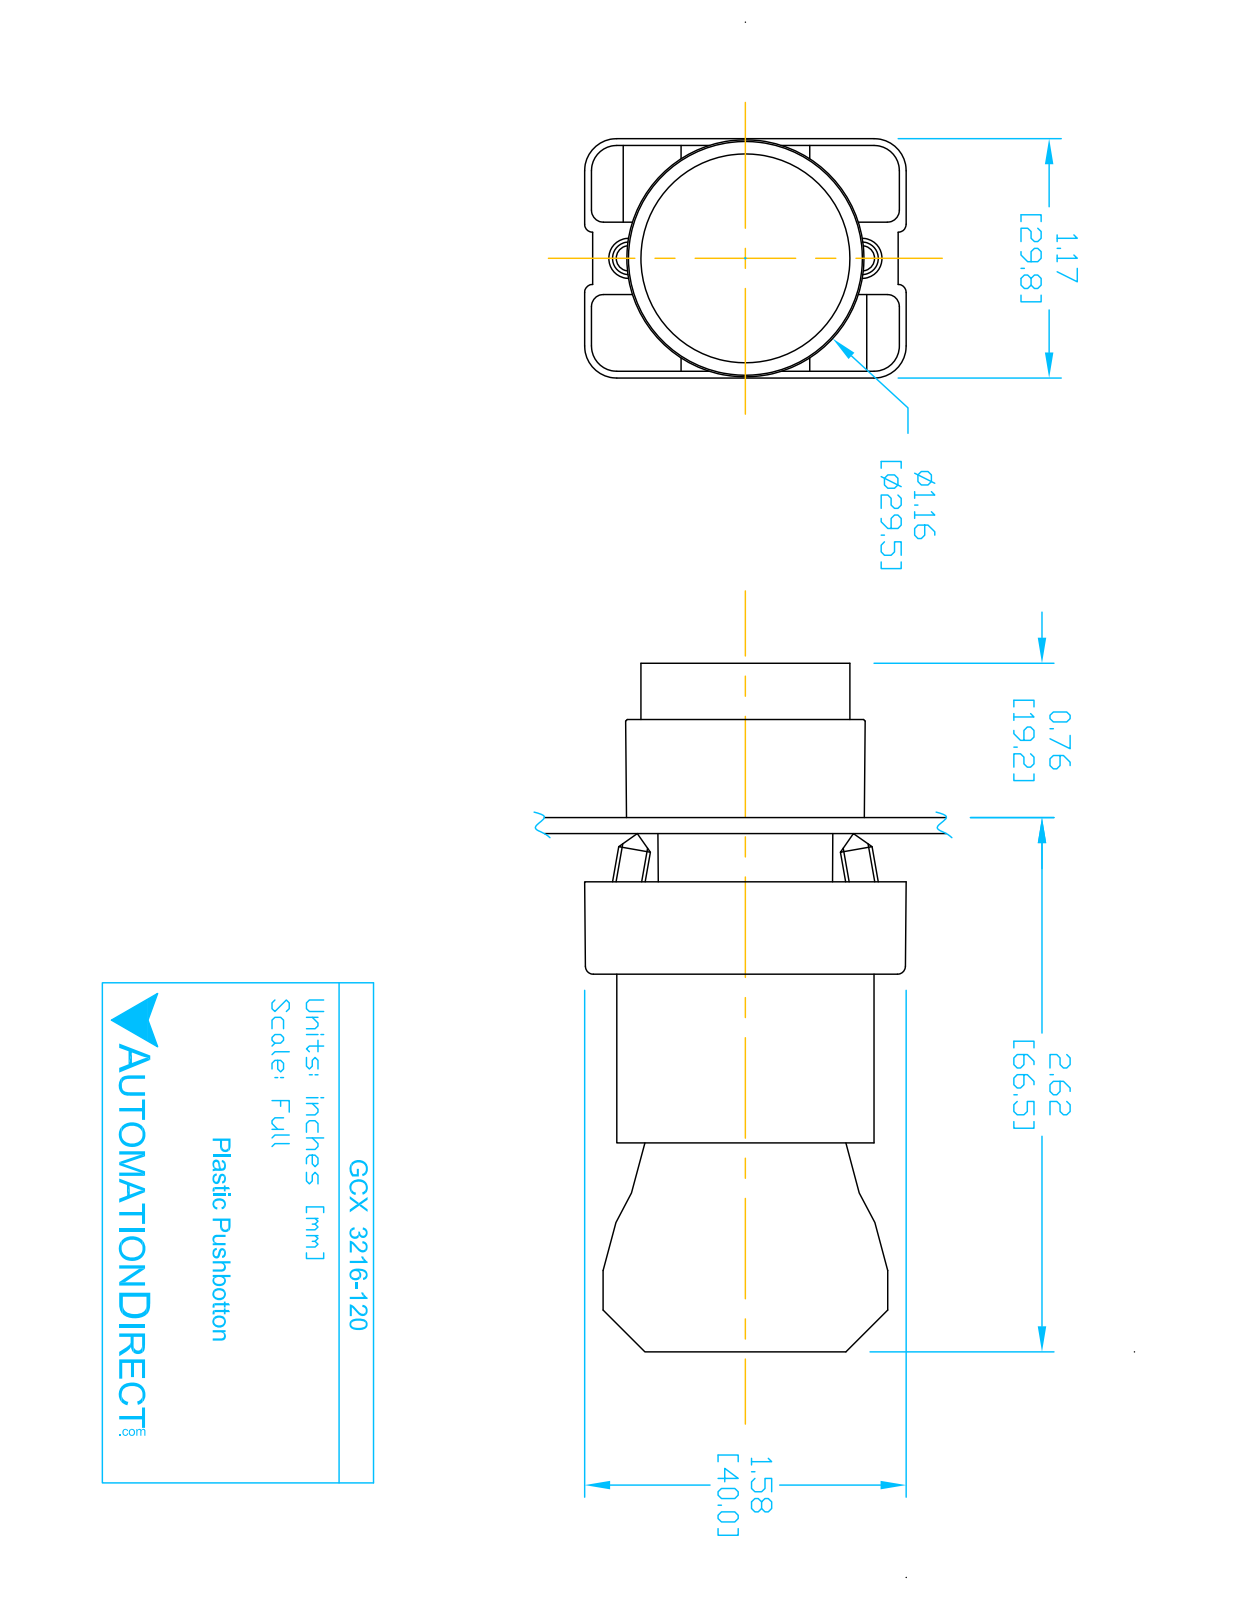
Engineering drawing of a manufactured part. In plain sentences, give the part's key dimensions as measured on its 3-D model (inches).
The part is named "ecx1040; ECX3029-2; GCX3216-120; ECX1050 (+1 more)". Its 3-D file was written by "SolidWorks 2016 (AUTOMOTIVE_DESIGN)". It is 7 solids with 425 faces: 250 planar, 144 cylindrical and 31 other. Overall it measures 3.319 by 1.581 by 1.177 inches. Its volume is 2.721 cubic inches and its surface area 36.32 square inches. Round holes: 2 of diameter 0.079, 2 of diameter 0.124, 2 of diameter 0.13, 1 of diameter 0.087, 1 of diameter 0.197, 1 of diameter 0.469, 1 of diameter 0.878, 1 of diameter 0.888, 1 of diameter 1.024. Round bosses or shafts: 4 of diameter 0.157, 1 of diameter 1.175, 1 of diameter 1.004, 1 of diameter 0.945, 1 of diameter 0.856, 1 of diameter 0.78, 1 of diameter 0.504. Partial cylindrical surfaces (rounded edges, fillets, slot ends): 24 of radius 0.059, 12 of radius 0.041, 12 of radius 0.124, 12 of radius 0.157, 8 of radius 0.039, 2 of radius 0.128, 1 of radius 0.02, 1 of radius 0.063. The main face-to-face distances are 0.827, 0.579, 1.171, 2.02, 1.193, 0.031, 0.033, 0.573, 1.165, 0.593. The hole center spacings are 0.236, 0.544, 0.472, 0.49.
